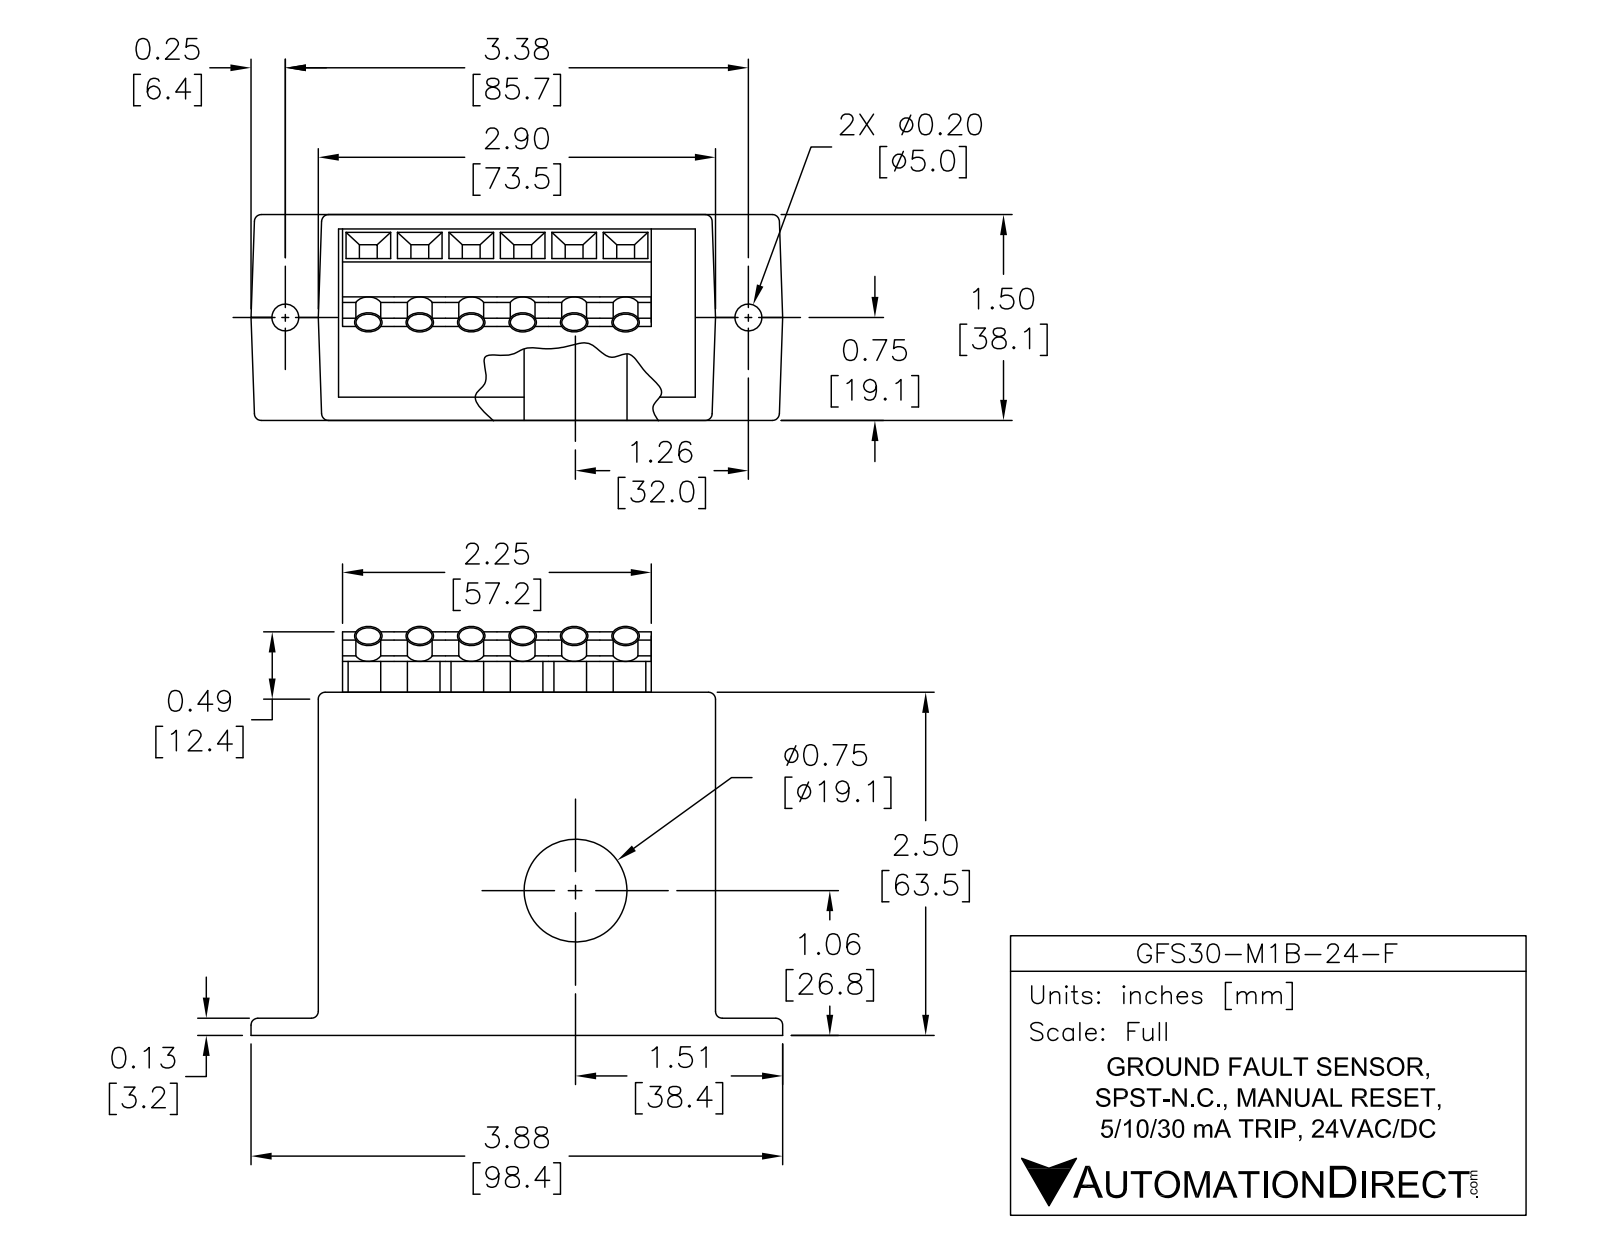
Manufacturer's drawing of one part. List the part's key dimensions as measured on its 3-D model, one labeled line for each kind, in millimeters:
Part name (STEP PRODUCT): GFS30-M1B-24-F
STEP written by: SolidWorks 2019 (AUTOMOTIVE_DESIGN)
Units: millimetres
Bodies: 19 solids, 312 faces (252 planar, 56 cylindrical, 4 other)
Overall size (bounding box): 98.4 × 73.9 × 38.2
Volume: 173 000 mm³ · Surface area: 35 150 mm²
Round holes (diameter × count): ⌀5.2 ×6, ⌀5 ×2, ⌀5.1 ×2, ⌀19.1 ×1
Round bosses / shafts (diameter × count): ⌀4.7 ×6
Partial cylindrical surfaces — rounded edges, fillets, slot ends (radius × count): R3.3 ×6
Main face-to-face distances: 38.1, 73.5, 2.5, 62.4, 59.8, 38.2, 2.6, 62.5, 1.1, 59.3
Hole centre spacings: 19, 9, 10, 9.4, 9.5, 17.3, 19.5, 26
